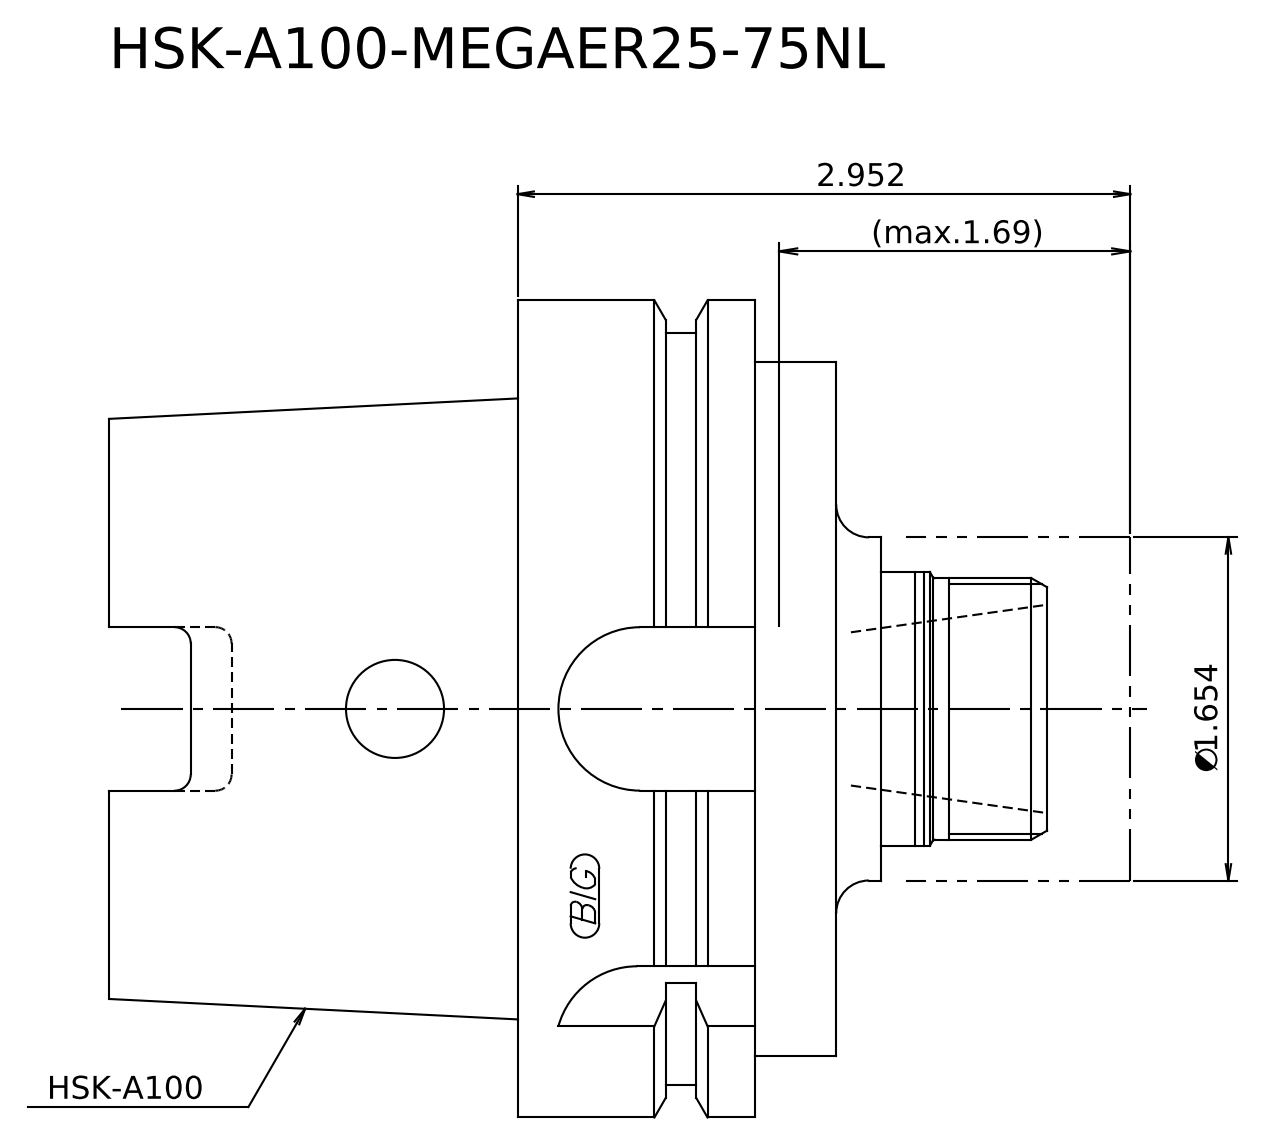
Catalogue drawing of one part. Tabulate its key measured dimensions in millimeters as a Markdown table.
| quantity | value |
| --- | --- |
| STEP written by | Kubotek KeyCreator 2011 V10.0.2 (22737) (automotive_design) |
| units | millimeters |
| bodies | 2 solids, 24 faces (10 planar, 8 cylindrical, 6 other) |
| overall size | 125 × 100 × 100 |
| volume | 554 757 mm³ |
| surface area | 48 933 mm² |
| round bosses / shafts (diameter × count) | 100 × 1, 92 × 1, 85 × 1, 42 × 1, 33.5 × 1, 32 × 1 |
| main face-to-face distances | 89, 39, 50, 10, 29, 79, 8.5, 18.5, 47.5, 97.5 |
